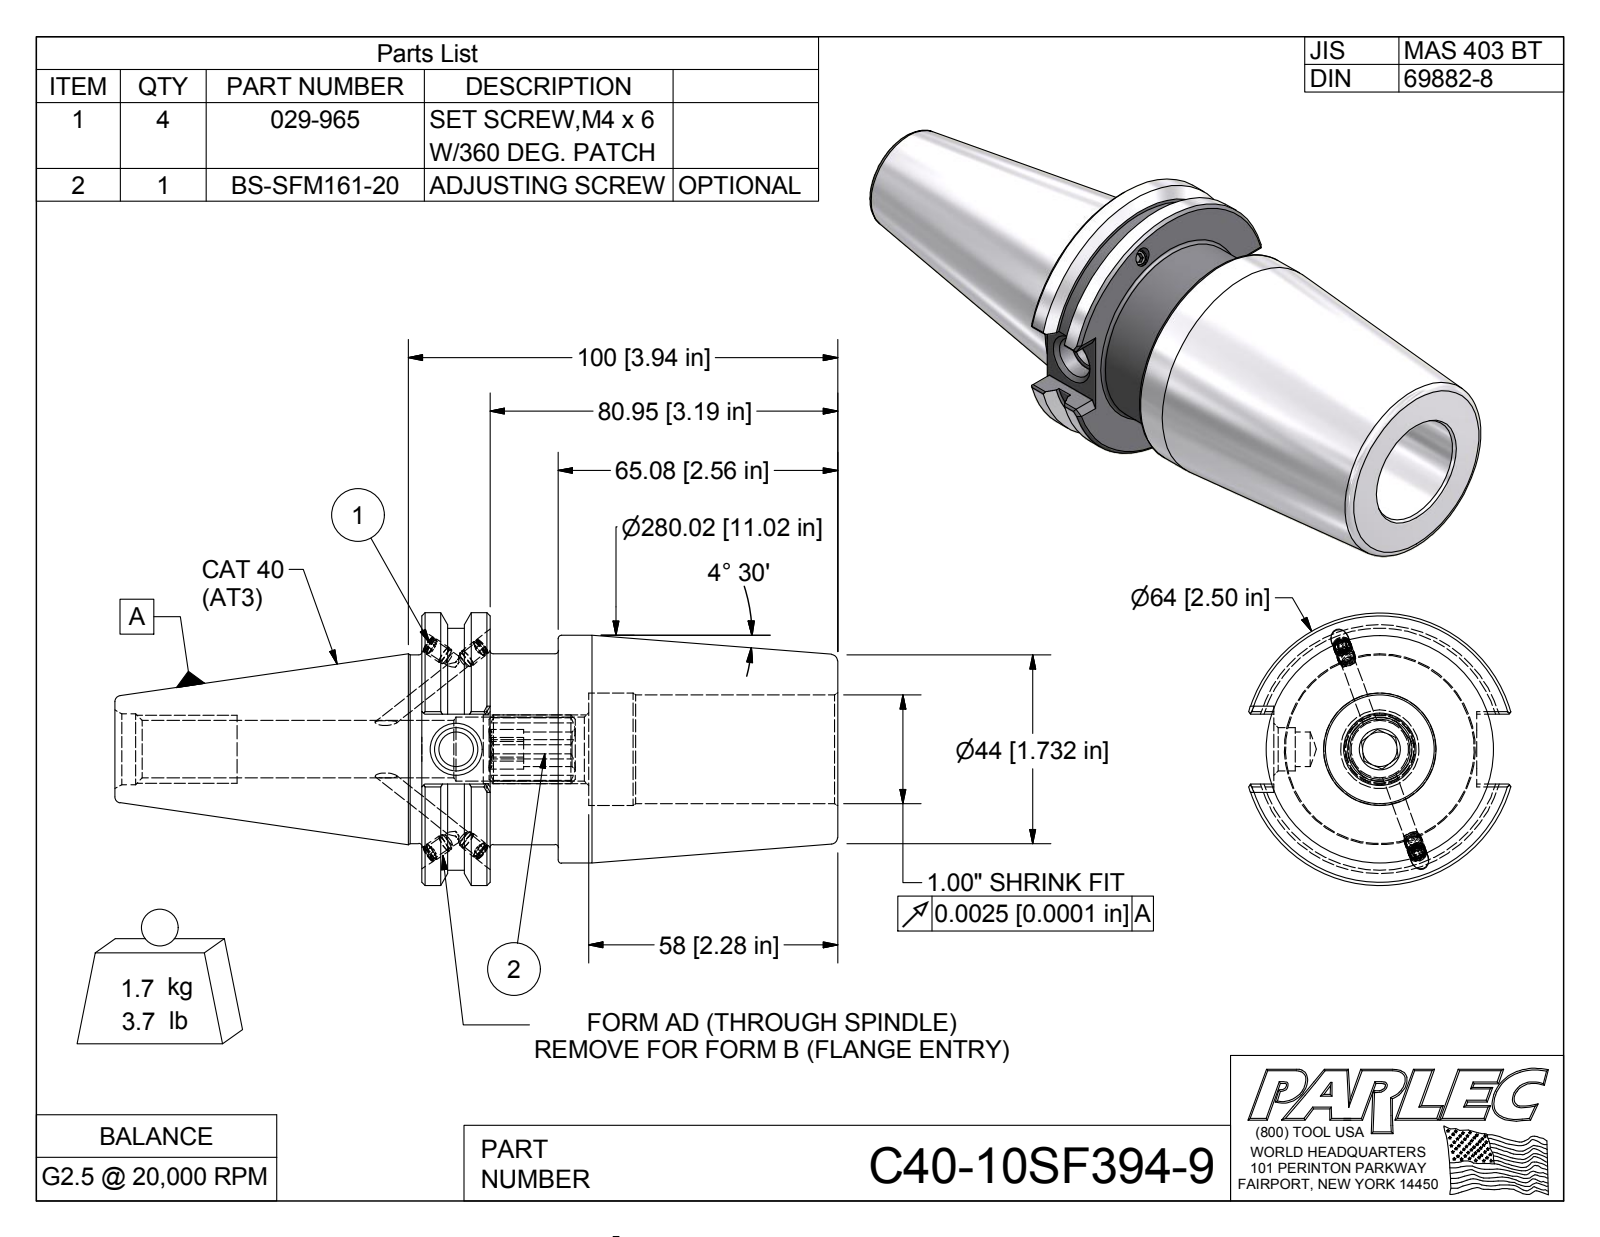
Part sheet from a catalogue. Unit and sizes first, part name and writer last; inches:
Units: inches
Overall size (bounding box): 6.625 × 2.5 × 2.403
Round holes (diameter × count): ⌀0.13 ×4, ⌀0.161 ×4, ⌀0.999 ×1, ⌀1.029 ×1
Round bosses / shafts (diameter × count): ⌀0.165 ×4, ⌀0.157 ×4, ⌀2.5 ×1, ⌀2.219 ×1, ⌀2.087 ×1, ⌀1.75 ×1, ⌀1.73 ×1
Partial cylindrical surfaces — rounded edges, fillets, slot ends (radius × count): R0.315 ×1
Main face-to-face distances: 0.625, 3.812, 3.187, 1.25, 2.562, 1.529, 0.904, 0.278, 2.283, 0.64
Volume: 13.22 in³ · Surface area: 64.39 in²
Bodies: 6 solids, 176 faces (88 planar, 33 cylindrical, 55 other)
Part name (STEP PRODUCT): C40-10SF394-9; C40BC-10SF394-9-1; 029-965; BS-SFM161-20
STEP written by: Autodesk Inventor 2009 (AUTOMOTIVE_DESIGN)
